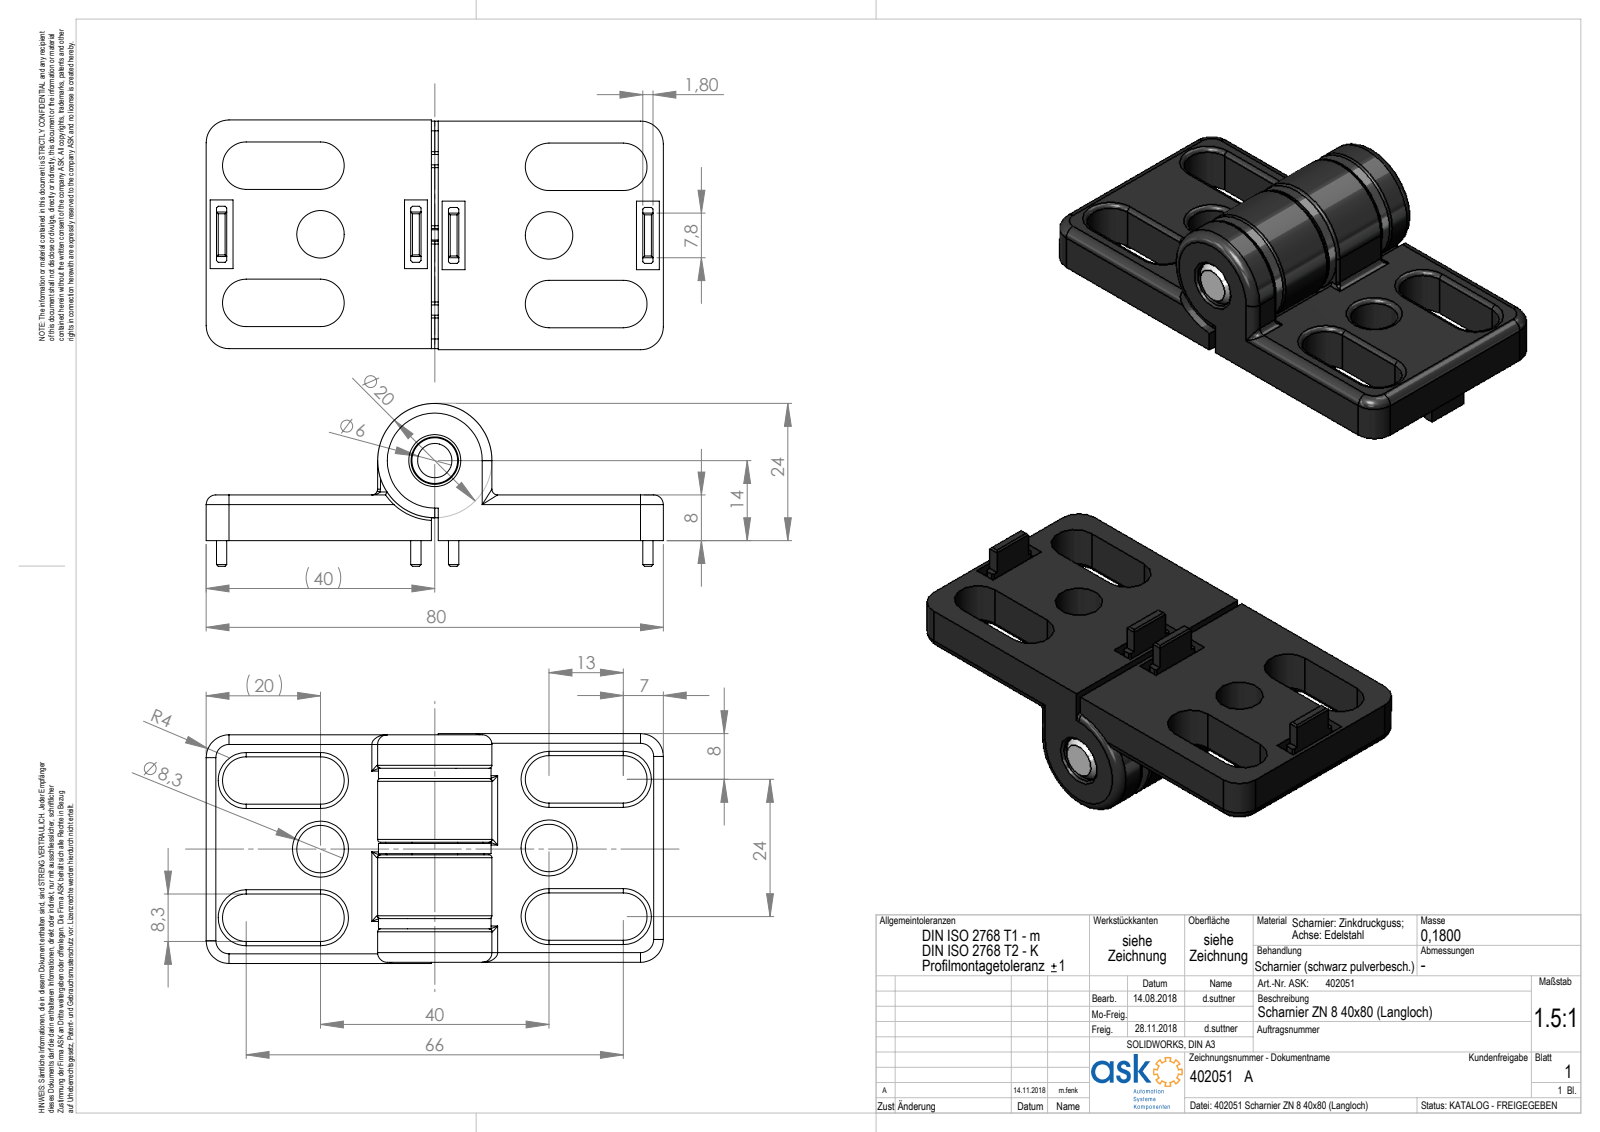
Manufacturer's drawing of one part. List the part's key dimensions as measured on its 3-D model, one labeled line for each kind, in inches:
Part name (STEP PRODUCT): 095310n08r_095 310 n8; 095z-01_095z.01; 402051_Scharnier ZN 8 40x80 (Langloch); 095z-02_095Z.02
STEP written by: SolidWorks 2017 (CONFIG_CONTROL_DESIGN)
Units: inches
Bodies: 6 solids, 292 faces (130 planar, 96 cylindrical, 66 other)
Overall size (bounding box): 3.15 × 1.583 × 1.122
Volume: 1.791 in³ · Surface area: 26.24 in²
Round holes (diameter × count): ⌀0.327 ×3, ⌀0.311 ×1
Round bosses / shafts (diameter × count): ⌀0.787 ×1, ⌀0.776 ×1, ⌀0.315 ×1
Partial cylindrical surfaces — rounded edges, fillets, slot ends (radius × count): R0.02 ×18, R0.067 ×10, R0.03 ×8, R0.163 ×8, R0.157 ×4, R0.039 ×2, R0.413 ×1
Main face-to-face distances: 0.071, 0.315, 0.518, 1.035, 0.748, 0.827, 0.596, 0.23, 0.301, 1.266
Hole centre spacings: 1.575
